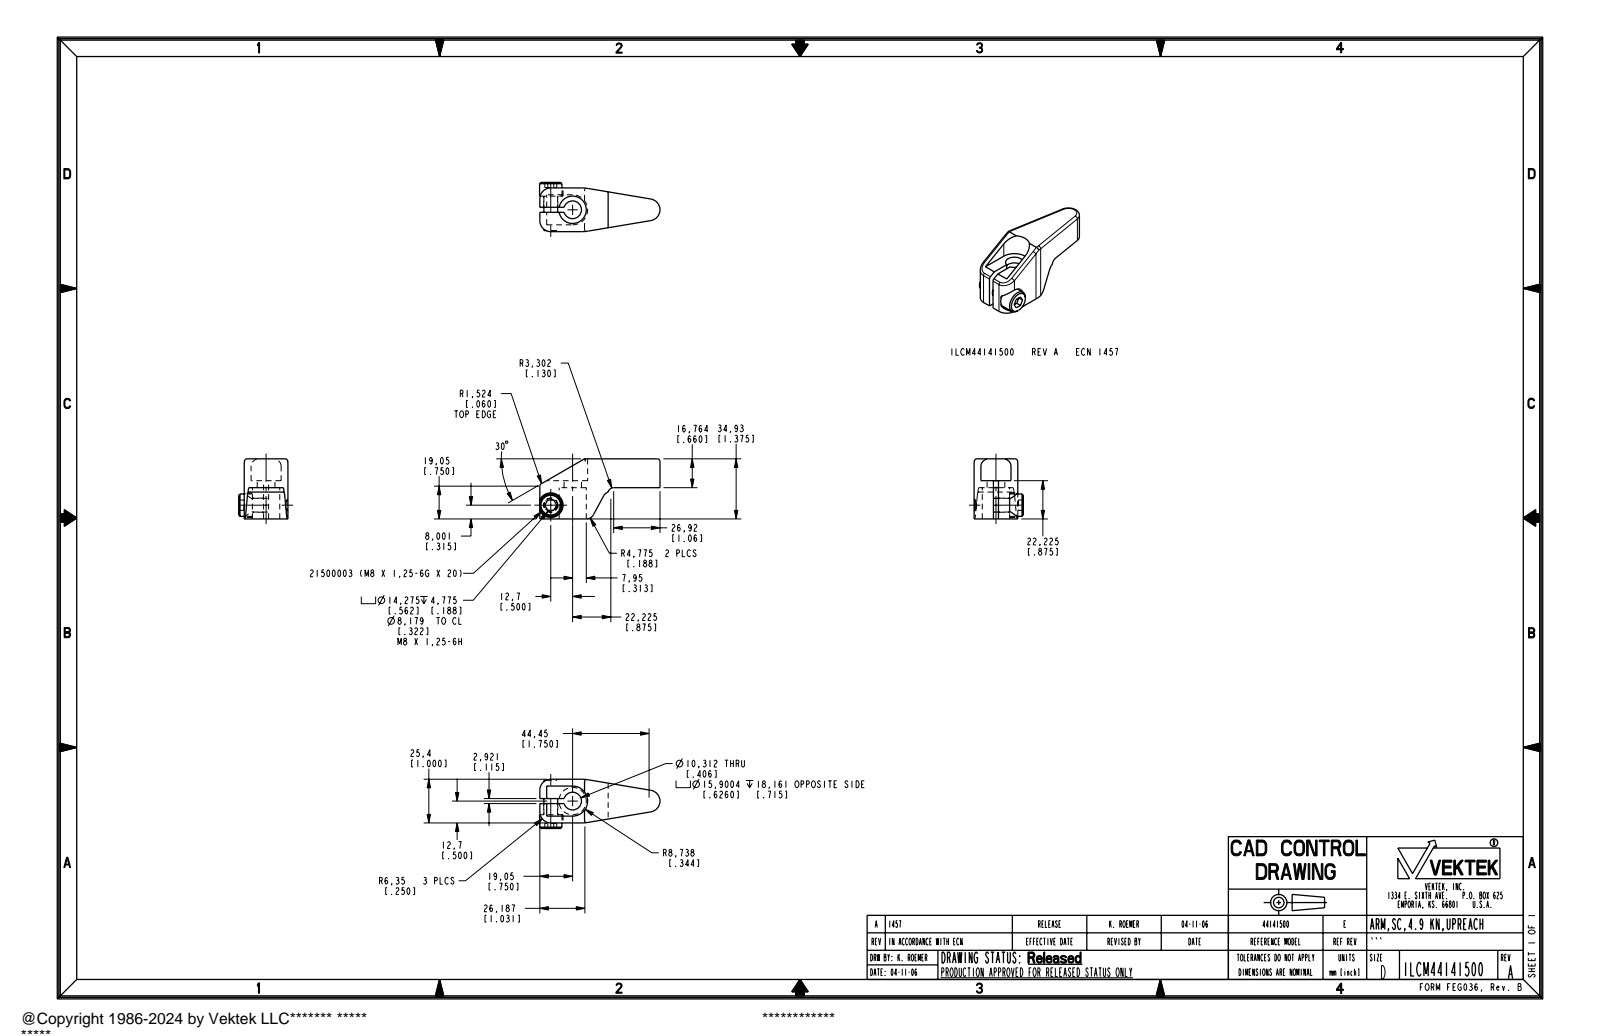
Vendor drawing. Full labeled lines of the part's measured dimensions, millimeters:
Part name (STEP PRODUCT): ILCM44141500
STEP written by: PRO/ENGINEER BY PARAMETRIC TECHNOLOGY CORPORATION, 2004290 (AUTOMOTIVE_DESIGN_CC2)
Units: millimetres
Bodies: 1 solid, 66 faces (31 planar, 26 cylindrical, 9 other)
Overall size (bounding box): 70 × 34.93 × 28.62
Volume: 27 926 mm³ · Surface area: 9 218 mm²
Round holes (diameter × count): ⌀6.78 ×1, ⌀8.18 ×1, ⌀10.31 ×1, ⌀14.27 ×1, ⌀15.9 ×1
Round bosses / shafts (diameter × count): ⌀13 ×1, ⌀8 ×1
Partial cylindrical surfaces — rounded edges, fillets, slot ends (radius × count): R1.52 ×5, R6.35 ×3, R4.78 ×2, R25.4 ×2, R3.3 ×1, R8.74 ×1
Main face-to-face distances: 34.93, 11.24, 14.16, 16.76, 18.17, 25.4, 12.71, 4.05, 22.22, 2.92
